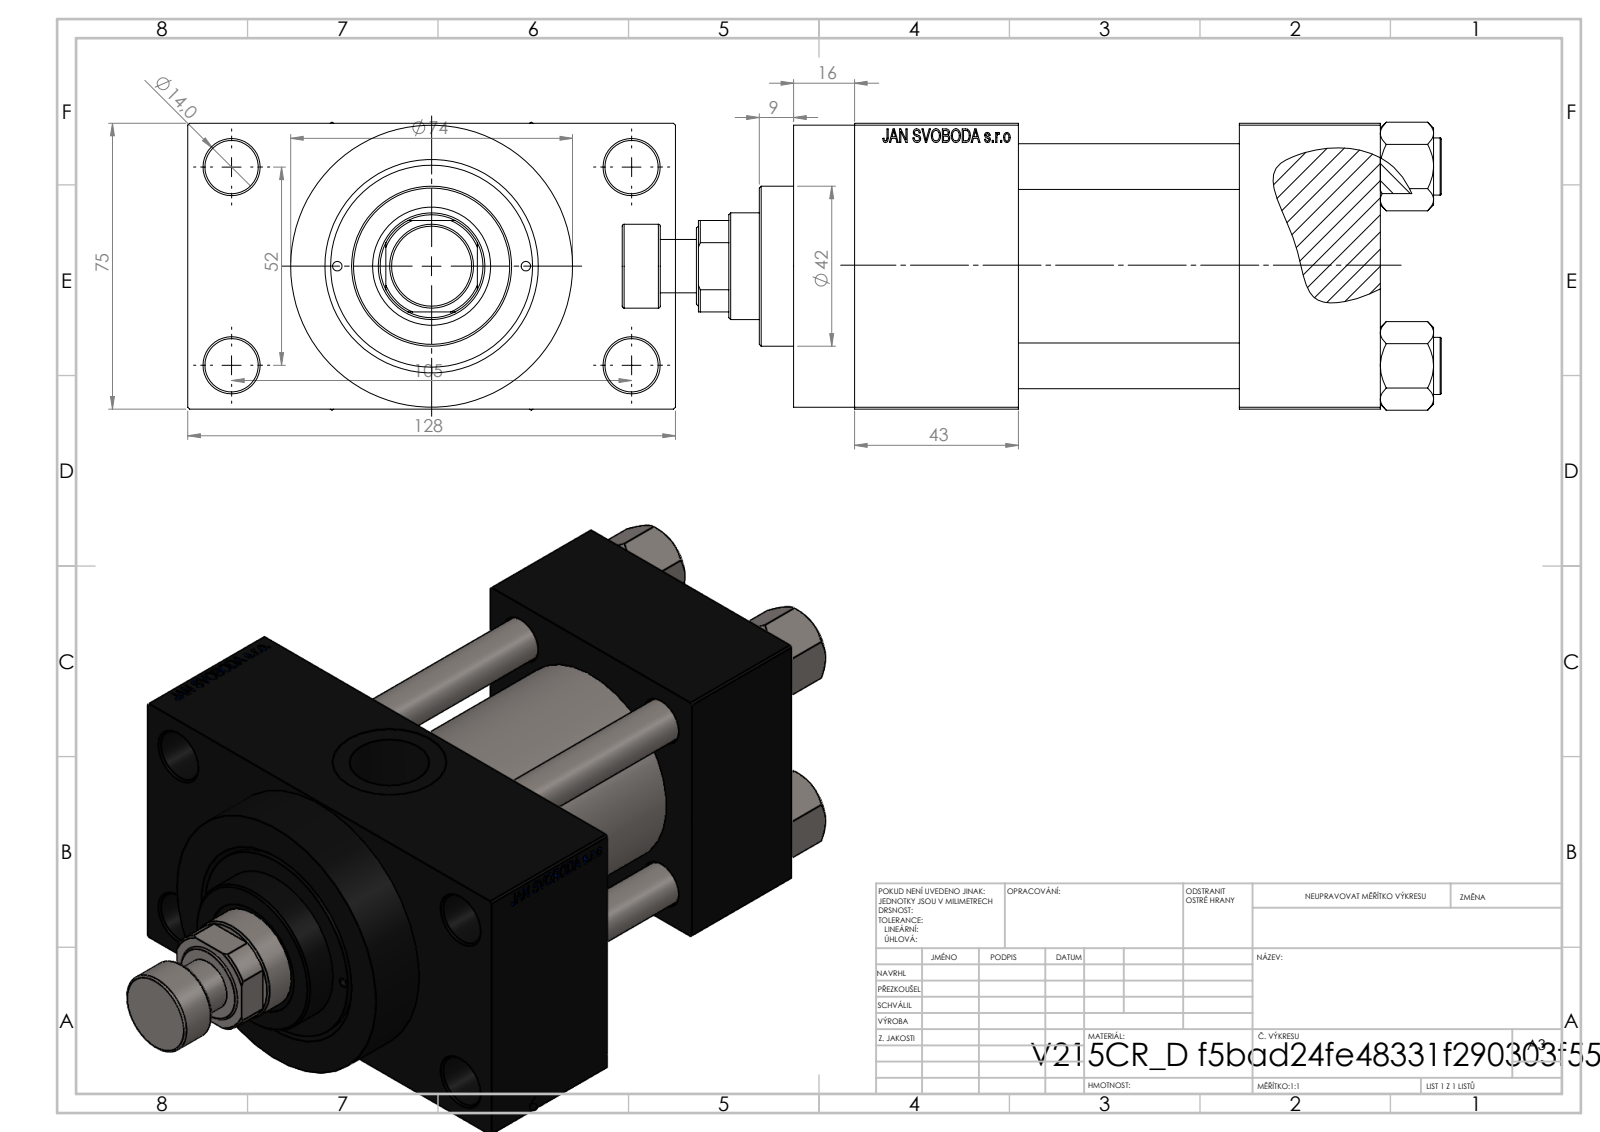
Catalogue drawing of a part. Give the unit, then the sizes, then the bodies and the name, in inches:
Units: inches
Overall size (bounding box): 8.465 × 5.039 × 2.974
Round holes (diameter × count): ⌀0.472 ×4, ⌀0.551 ×4, ⌀0.098 ×2, ⌀0.276 ×2, ⌀0.825 ×2, ⌀1.181 ×2, ⌀0.728 ×1, ⌀1.102 ×1, ⌀1.22 ×1, ⌀1.614 ×1, ⌀1.969 ×1, ⌀2.087 ×1
Round bosses / shafts (diameter × count): ⌀0.591 ×4, ⌀2.913 ×1, ⌀2.205 ×1, ⌀1.654 ×1, ⌀0.866 ×1, ⌀0.551 ×1
Partial cylindrical surfaces — rounded edges, fillets, slot ends (radius × count): R0.531 ×1
Main face-to-face distances: 2.953, 2.283, 1.457, 3.74, 1.043, 3.996, 5.433, 3.976, 1.693, 0.63
Hole centre spacings: 1.031, 1.037, 1.456, 1.497, 2.059, 2.253, 2.3, 2.307
Volume: 50.07 in³ · Surface area: 265.1 in²
Bodies: 12 solids, 1126 faces (503 planar, 97 cylindrical, 526 other)
Part name (STEP PRODUCT): V215CR_VCP_D; V215_VC_A; V215CR_D_TYCINKA; V215CR_D_Body (+2 more)
STEP written by: SolidWorks 2019 (CONFIG_CONTROL_DESIGN)
